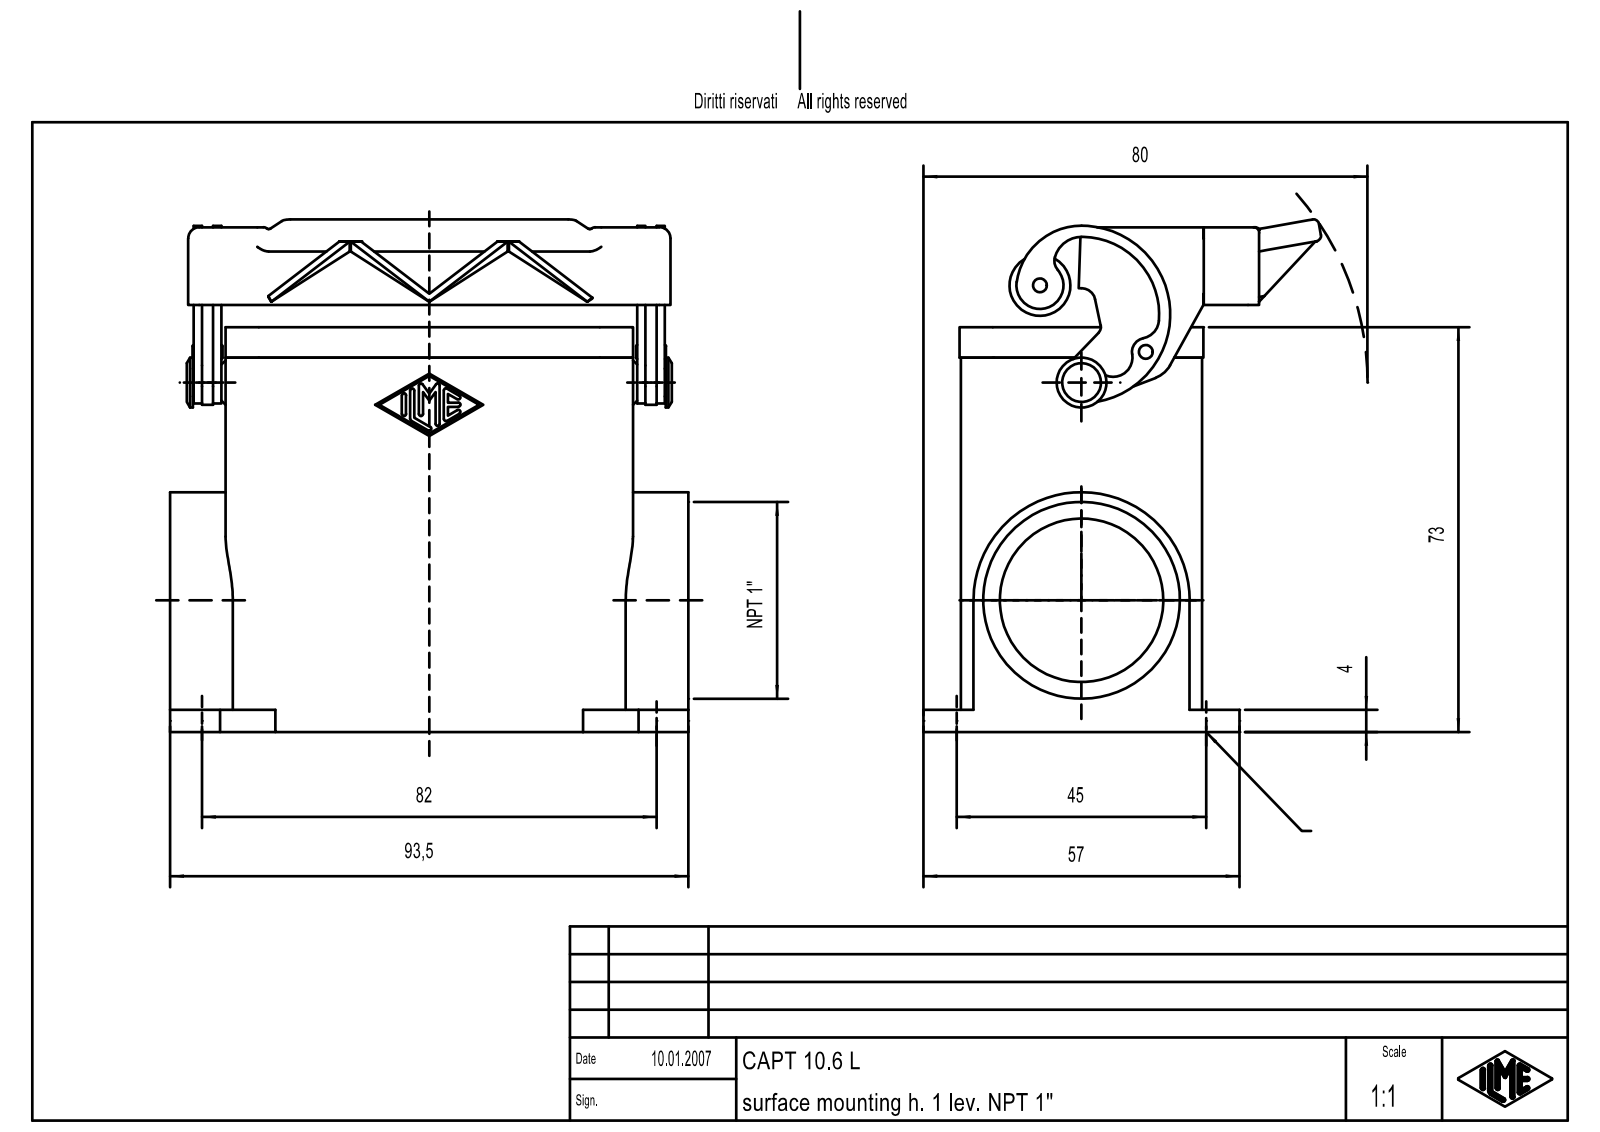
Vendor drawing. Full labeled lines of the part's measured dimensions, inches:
Part name (STEP PRODUCT): p1; p2; p3; p4 (+2 more)
STEP written by: Creo Elements/Direct Modeling 18.0B 02-Dec-2011 (C) Parametric Technology GmbH (AUTOMOTIVE_DESIGN)
Units: inches
Bodies: 4 solids, 405 faces (205 planar, 152 cylindrical, 48 other)
Overall size (bounding box): 3.681 × 3.639 × 2.823
Volume: 6.257 in³ · Surface area: 84.87 in²
Round holes (diameter × count): ⌀0.097 ×4, ⌀0.118 ×4, ⌀0.217 ×4, ⌀0.079 ×1, ⌀1.161 ×1, ⌀1.397 ×1
Round bosses / shafts (diameter × count): ⌀0.433 ×1, ⌀0.354 ×1, ⌀0.197 ×1, ⌀0.118 ×1, ⌀0.098 ×1
Partial cylindrical surfaces — rounded edges, fillets, slot ends (radius × count): R0.015 ×14, R0.079 ×12, R0.236 ×8, R0.039 ×7, R0.059 ×5, R0.118 ×4, R0.098 ×3, R0.138 ×2
Main face-to-face distances: 0.118, 1.594, 0.157, 1.713, 1.476, 2.657, 0.463, 0.394, 2.5, 0.344
Hole centre spacings: 0.606, 1.5, 2.759, 3.081, 1.063, 1.772, 2.244, 2.483
